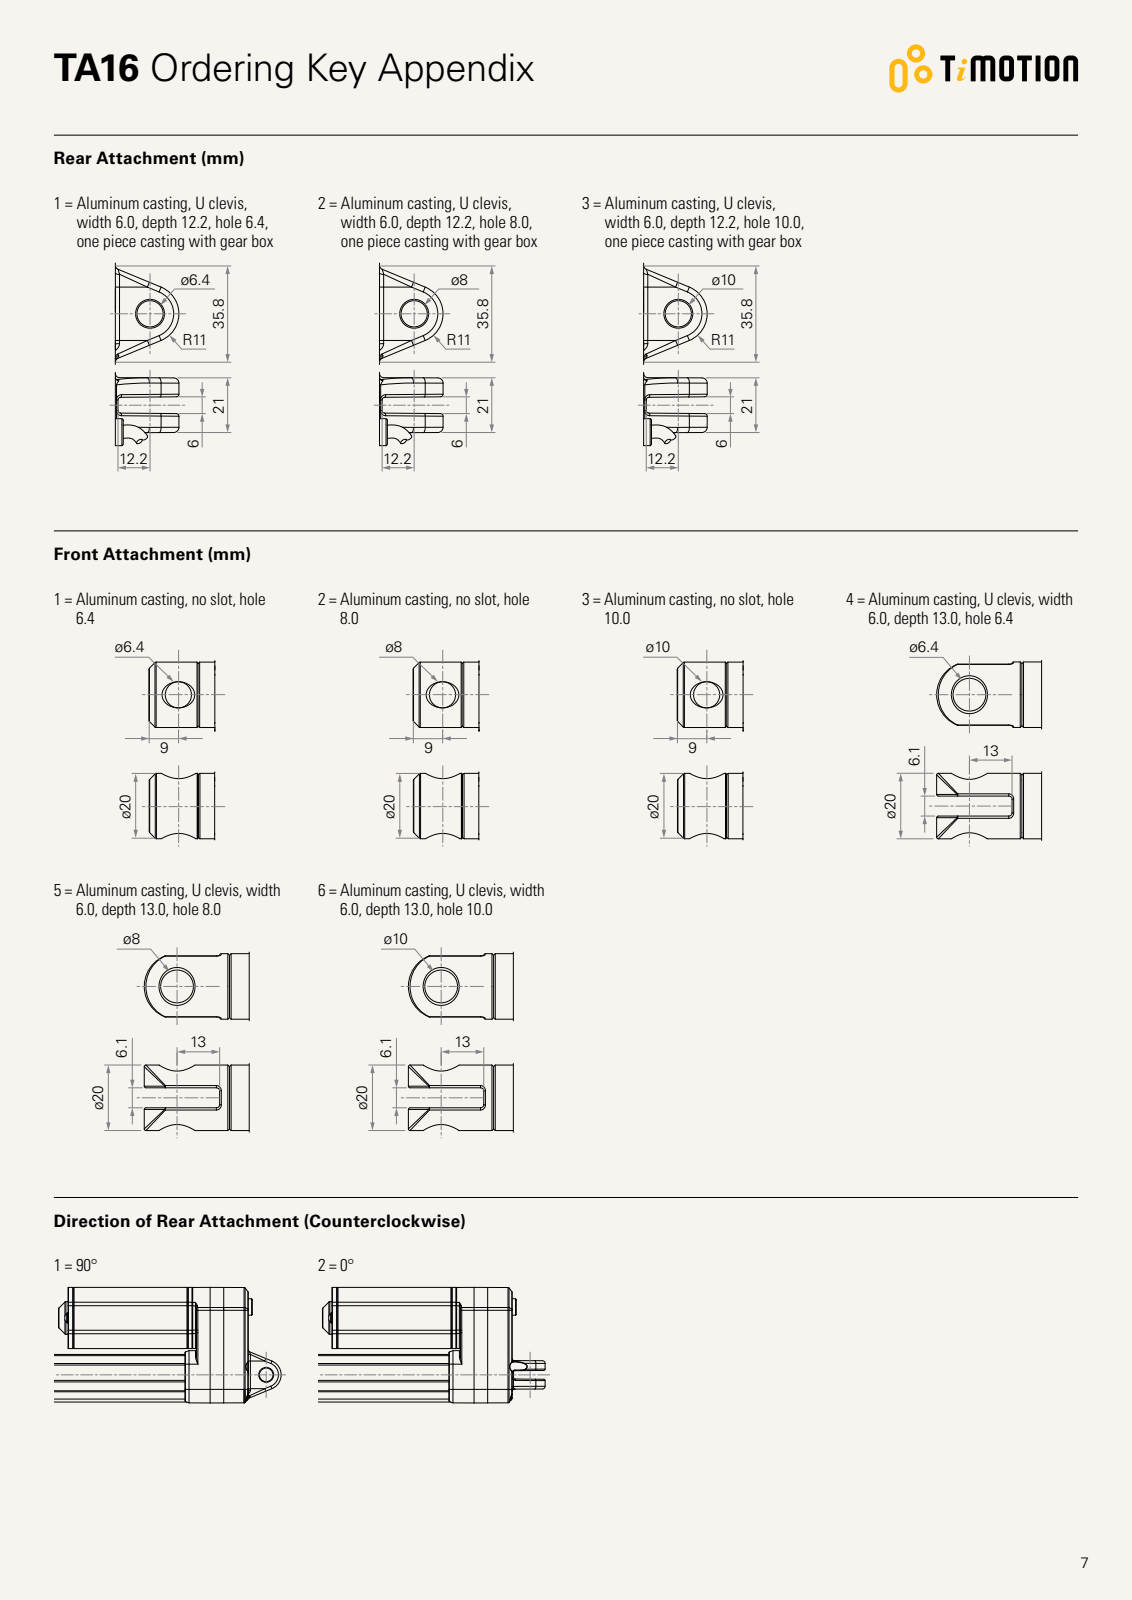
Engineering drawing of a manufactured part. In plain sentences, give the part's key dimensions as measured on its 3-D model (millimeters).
The part is named "產品三維模型圖-TA16（標準）-A". Its 3-D file was written by "SolidWorks 2015 (CONFIG_CONTROL_DESIGN)". It is 1 solid with 635 faces: 248 planar, 133 cylindrical and 254 other. Overall it measures 326.3 by 123.1 by 43.04 millimeters. Its volume is 475 800 cubic millimeters and its surface area 80 229 square millimeters. Round holes: 5 of diameter 4.2, 5 of diameter 7, 2 of diameter 8, 1 of diameter 15. Round bosses or shafts: 5 of diameter 6.8, 4 of diameter 6.6, 2 of diameter 7.5, 1 of diameter 24, 1 of diameter 20, 1 of diameter 5. Partial cylindrical surfaces (rounded edges, fillets, slot ends): 18 of radius 1, 8 of radius 0.4, 8 of radius 0.9, 7 of radius 0.5, 6 of radius 1.6, 6 of radius 3.6, 4 of radius 0.3, 4 of radius 2. The main face-to-face distances are 40, 42.92, 43, 132.4, 10.89, 32.03, 32.11, 140.1, 272.5, 46.5. The hole center spacings are 17.56, 20.18, 21.21, 36.62, 55.34, 75.04, 27, 33.
